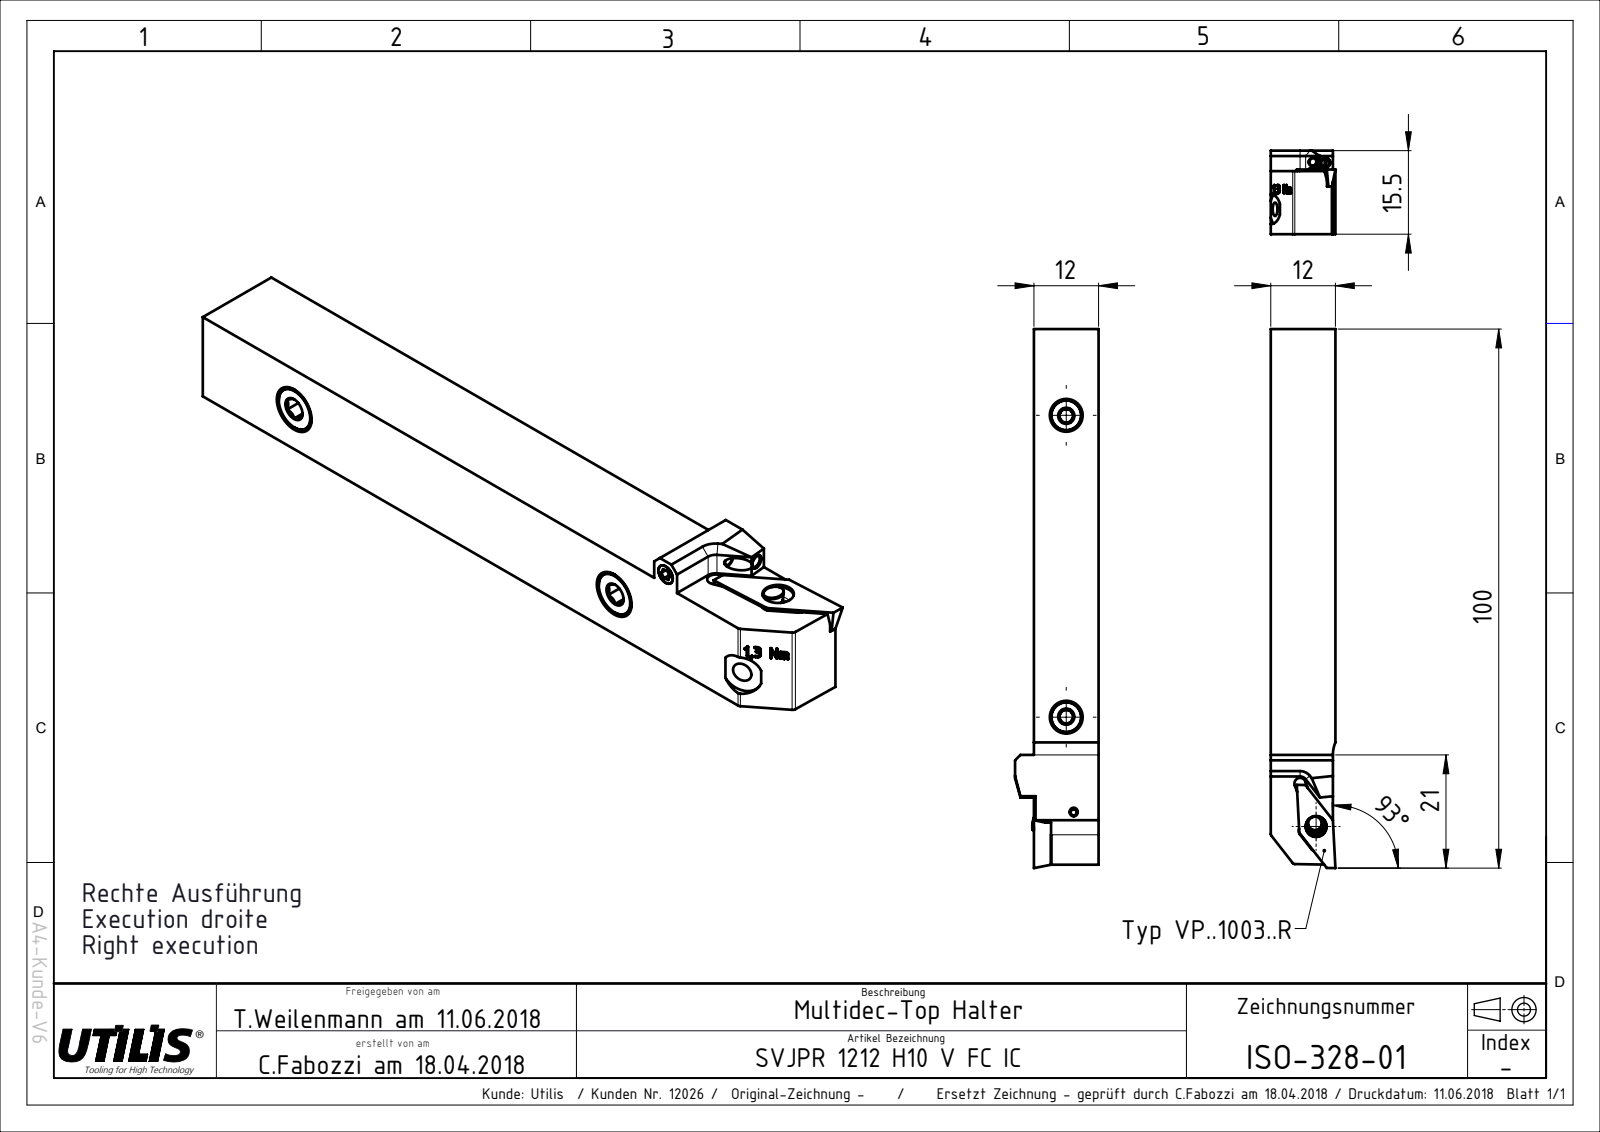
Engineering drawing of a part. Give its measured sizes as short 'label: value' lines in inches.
name: ISO-328-01
written by: SolidWorks 2017 (AUTOMOTIVE_DESIGN)
unit: in
bodies: 1 solid, 128 faces (63 planar, 12 cylindrical, 53 other)
size: 3.937 × 0.61 × 0.472
volume: 0.864 in³; area: 8.065 in²
rounds: 3× R0.041, 2× R0.02, 1× R0.052, 1× R0.108, 1× R0.236, 1× R0.24
face distances: 0.472, 0.454, 0.019, 0.461, 3.11, 0.61, 0.15, 0.138, 0.157, 3.268
